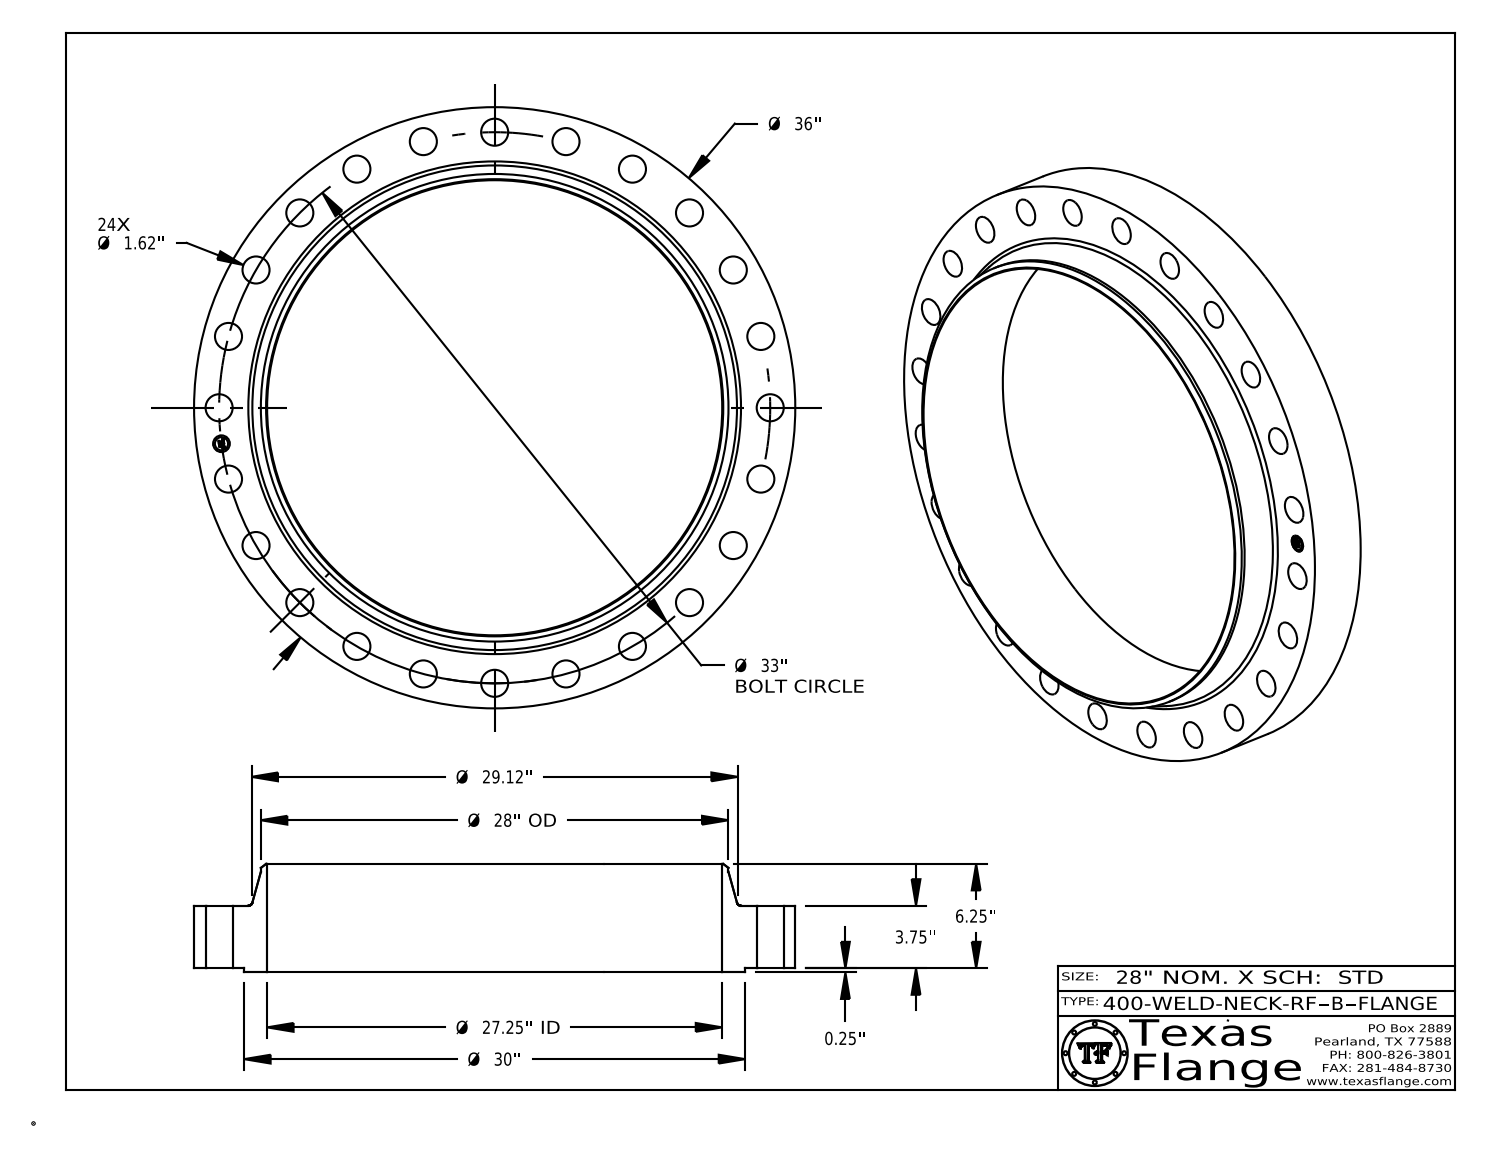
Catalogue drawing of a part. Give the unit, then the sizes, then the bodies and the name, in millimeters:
Units: millimetres
Overall size (bounding box): 914.4 × 914.4 × 165.1
Round holes (diameter × count): ⌀41.1 ×24, ⌀25.4 ×1, ⌀692.2 ×1
Round bosses / shafts (diameter × count): ⌀1.5 ×8, ⌀914.4 ×1, ⌀762 ×1, ⌀711.2 ×1, ⌀20 ×1
Main face-to-face distances: 95.3, 6.4, 101.6, 165.1, 158.8, 63.5, 101.2, 94.9, 0.4, 63.9
Hole centre spacings: 419.1, 109.4, 216.9, 510.3, 592.7, 665, 809.7, 831
Volume: 26 300 000 mm³ · Surface area: 1 545 000 mm²
Bodies: 1 solid, 451 faces (369 planar, 76 cylindrical, 6 other)
Part name (STEP PRODUCT): 400-WELD-NECK-RF, Series B
STEP written by: CATIA V5 STEP AP214 (AUTOMOTIVE_DESIGN)
